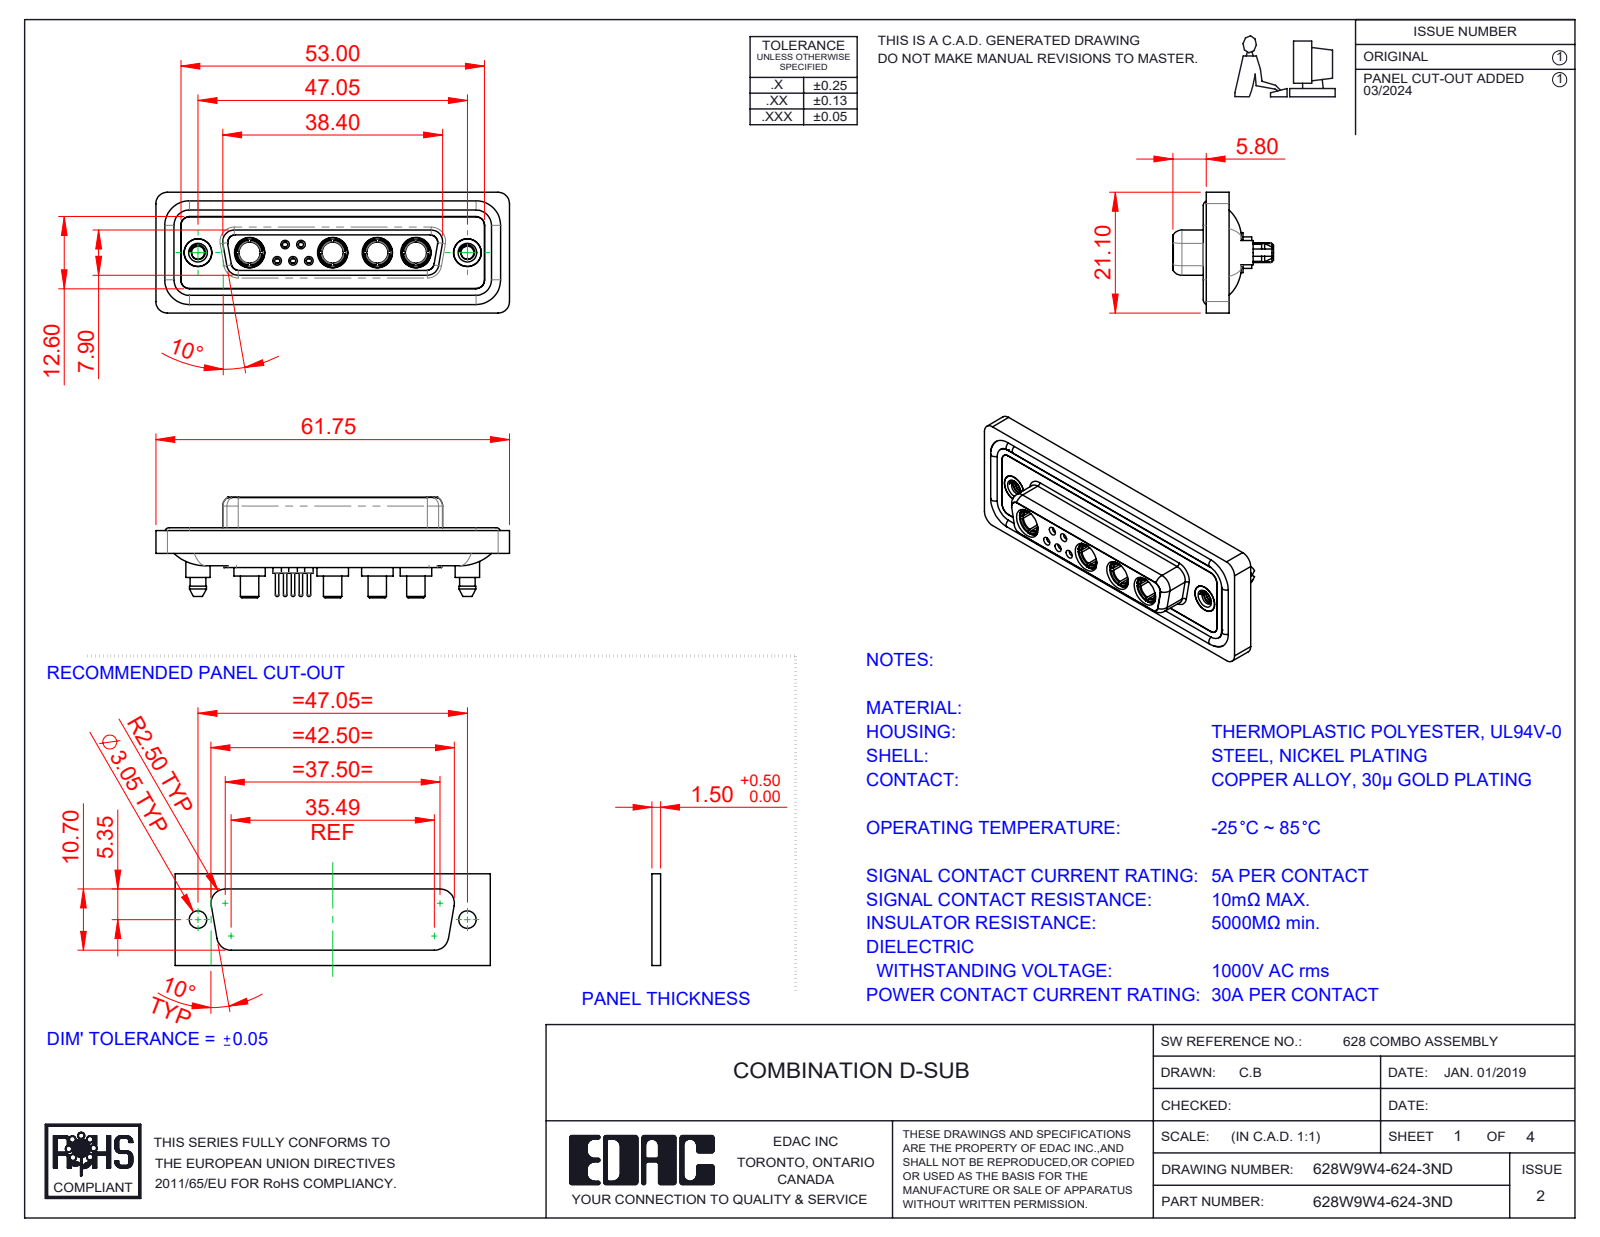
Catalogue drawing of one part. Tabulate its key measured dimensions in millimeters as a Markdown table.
| quantity | value |
| --- | --- |
| part name | 628W9W4-624-3ND; Power Socket_30A S; 628Combo Threaded Boardlock_D; 628Combo Housing_9W4 (+5 more) |
| STEP written by | SolidWorks 2023 (CONFIG_CONTROL_DESIGN) |
| units | millimeters |
| bodies | 20 solids, 1023 faces (312 planar, 423 cylindrical, 288 other) |
| overall size | 61.75 × 21.1 × 17.55 |
| volume | 8 387 mm³ |
| surface area | 13 920 mm² |
| round holes (diameter × count) | 4.85 × 6, 0.9 × 5, 1.1 × 5, 1.5 × 5, 2 × 5, 3.7 × 4, 5.3 × 4, 1.6 × 3, 1.7 × 2, 2.26 × 2, 4 × 2, 4.05 × 2 |
| round bosses / shafts (diameter × count) | 1.6 × 6, 2.2 × 5, 0.6 × 5, 5.5 × 4, 5.2 × 4, 4.96 × 4, 4.75 × 4, 3.75 × 4 |
| partial cylindrical surfaces (radius × count) | 1.5 × 24, 2 × 18, 1.6 × 10, 1.35 × 8, 0.25 × 4, 0.5 × 4, 0.6 × 4, 0.65 × 4 |
| main face-to-face distances | 0.4, 1.8, 7.45, 5.65, 0.5, 7.05, 6.6, 1.6, 1.1, 2.9 |
| hole center spacings | 3.16, 2.77, 5.03, 2.76, 4.4, 5.02, 5.54, 5.73 |
